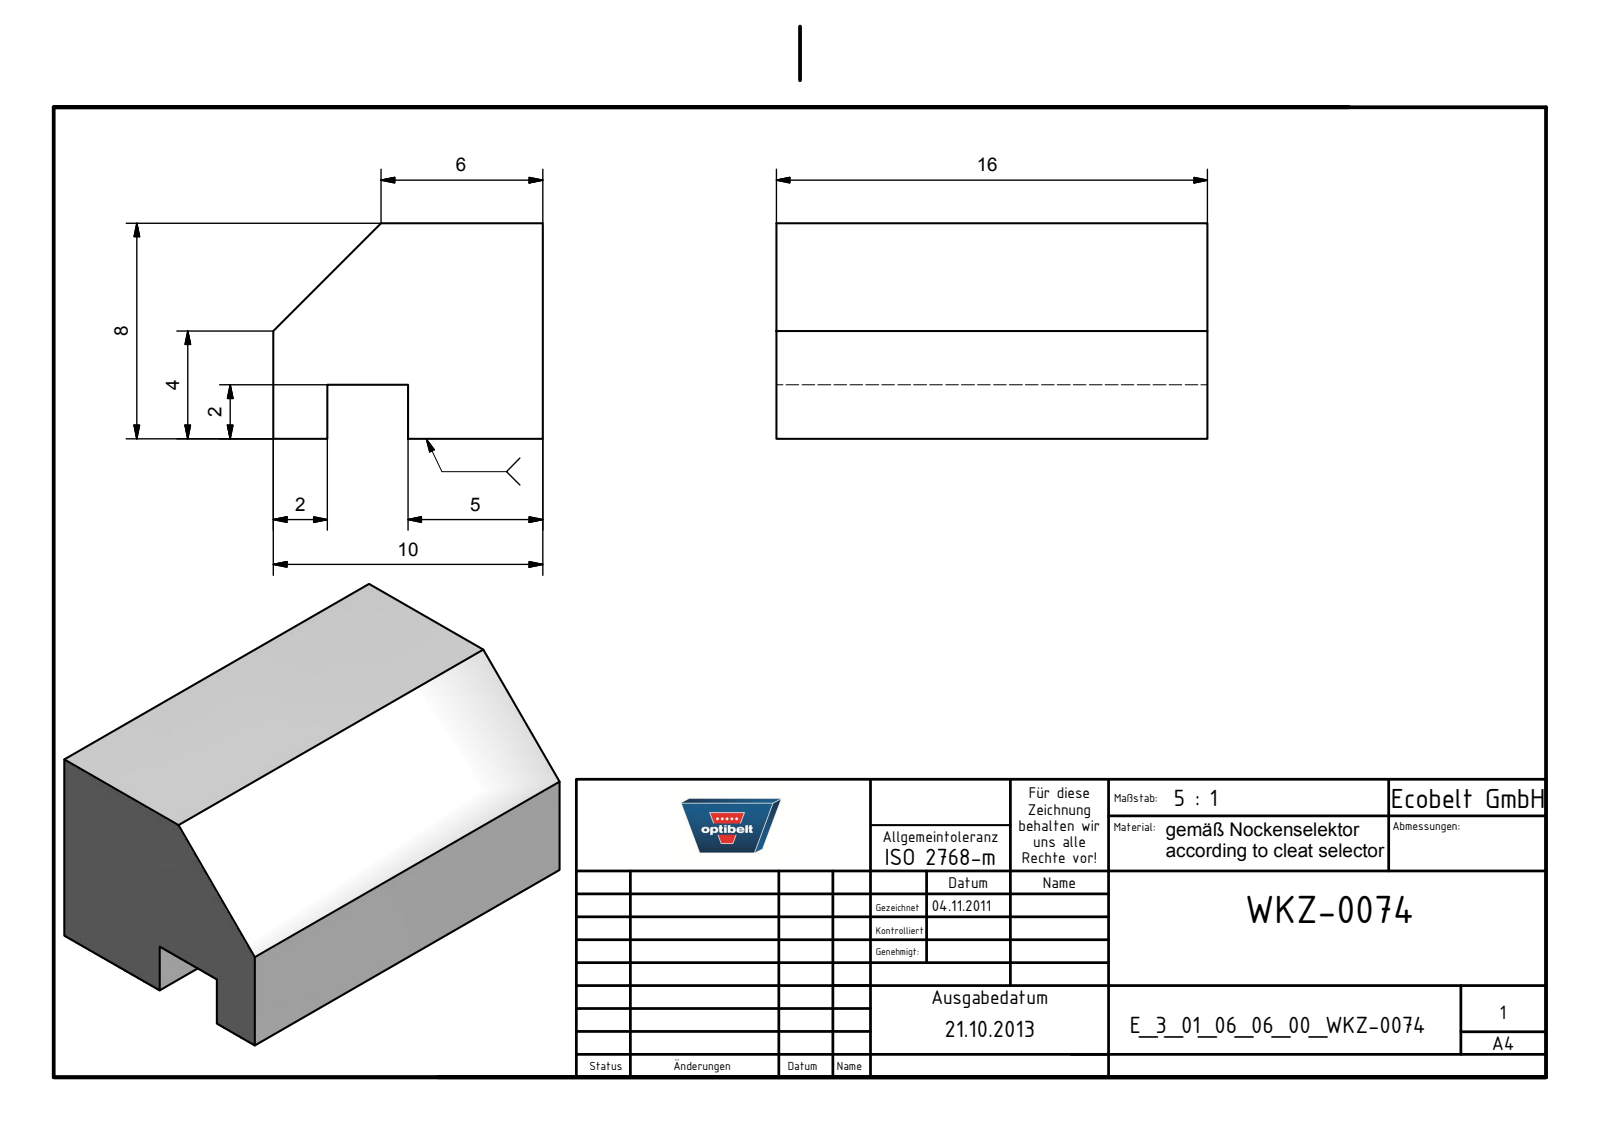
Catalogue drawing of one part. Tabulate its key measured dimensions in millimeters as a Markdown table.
| quantity | value |
| --- | --- |
| part name | E_3_01_06_06_00_WKZ-0074 |
| STEP written by | Autodesk Inventor 2025 (AUTOMOTIVE_DESIGN) |
| units | millimeters |
| bodies | 1 solid, 11 faces (11 planar, 0 cylindrical, 0 other) |
| overall size | 16 × 10 × 8 |
| volume | 1 056 mm³ |
| surface area | 735 mm² |
| main face-to-face distances | 8, 2, 16, 10, 5, 6, 3 |
